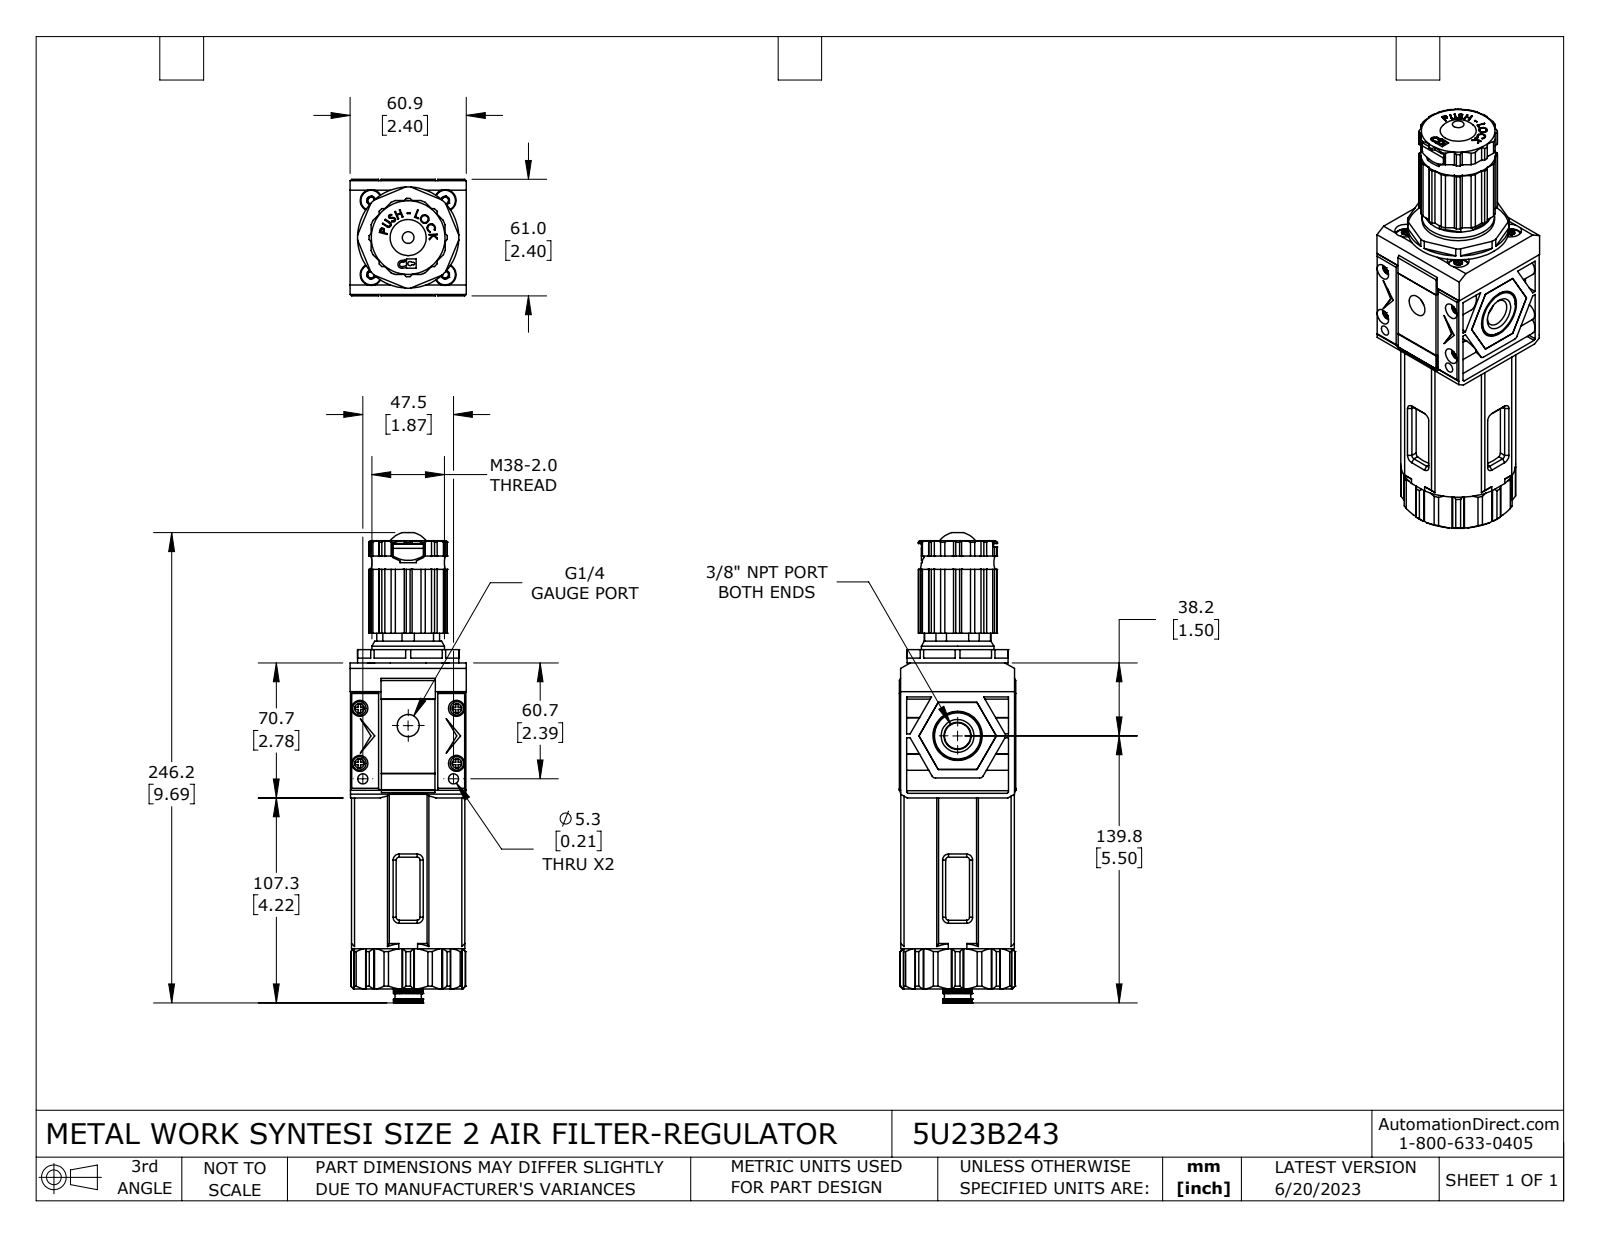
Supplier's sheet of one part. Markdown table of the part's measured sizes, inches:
| quantity | value |
| --- | --- |
| part name | 5U23B243 |
| STEP written by | SolidWorks 2021 (CONFIG_CONTROL_DESIGN) |
| units | inches |
| bodies | 15 solids, 1919 faces (1252 planar, 455 cylindrical, 212 other) |
| overall size | 9.693 × 2.402 × 2.398 |
| volume | 28.26 in³ |
| surface area | 213.7 in² |
| round holes (diameter × count) | 0.128 × 4, 0.165 × 4, 0.331 × 4, 0.449 × 4, 0.209 × 2, 0.126 × 1, 0.276 × 1, 0.343 × 1, 0.457 × 1, 1.25 × 1, 1.411 × 1, 1.508 × 1 |
| round bosses / shafts (diameter × count) | 0.276 × 4, 0.189 × 4, 0.15 × 4, 2.087 × 1, 1.496 × 1, 1.248 × 1, 1.035 × 1, 0.925 × 1 |
| partial cylindrical surfaces (radius × count) | 0.011 × 28, 0.02 × 16, 0.059 × 8, 0.069 × 4, 0.191 × 4, 0.807 × 4, 0.008 × 2, 0.079 × 2 |
| main face-to-face distances | 5.303, 2.39, 3.11, 3.205, 2.098, 1.13, 2.193, 2.402, 0.031, 5.894 |
| hole center spacings | 1.08, 1.528, 0.325, 1.057, 1.134, 1.265, 1.443, 1.454 |
